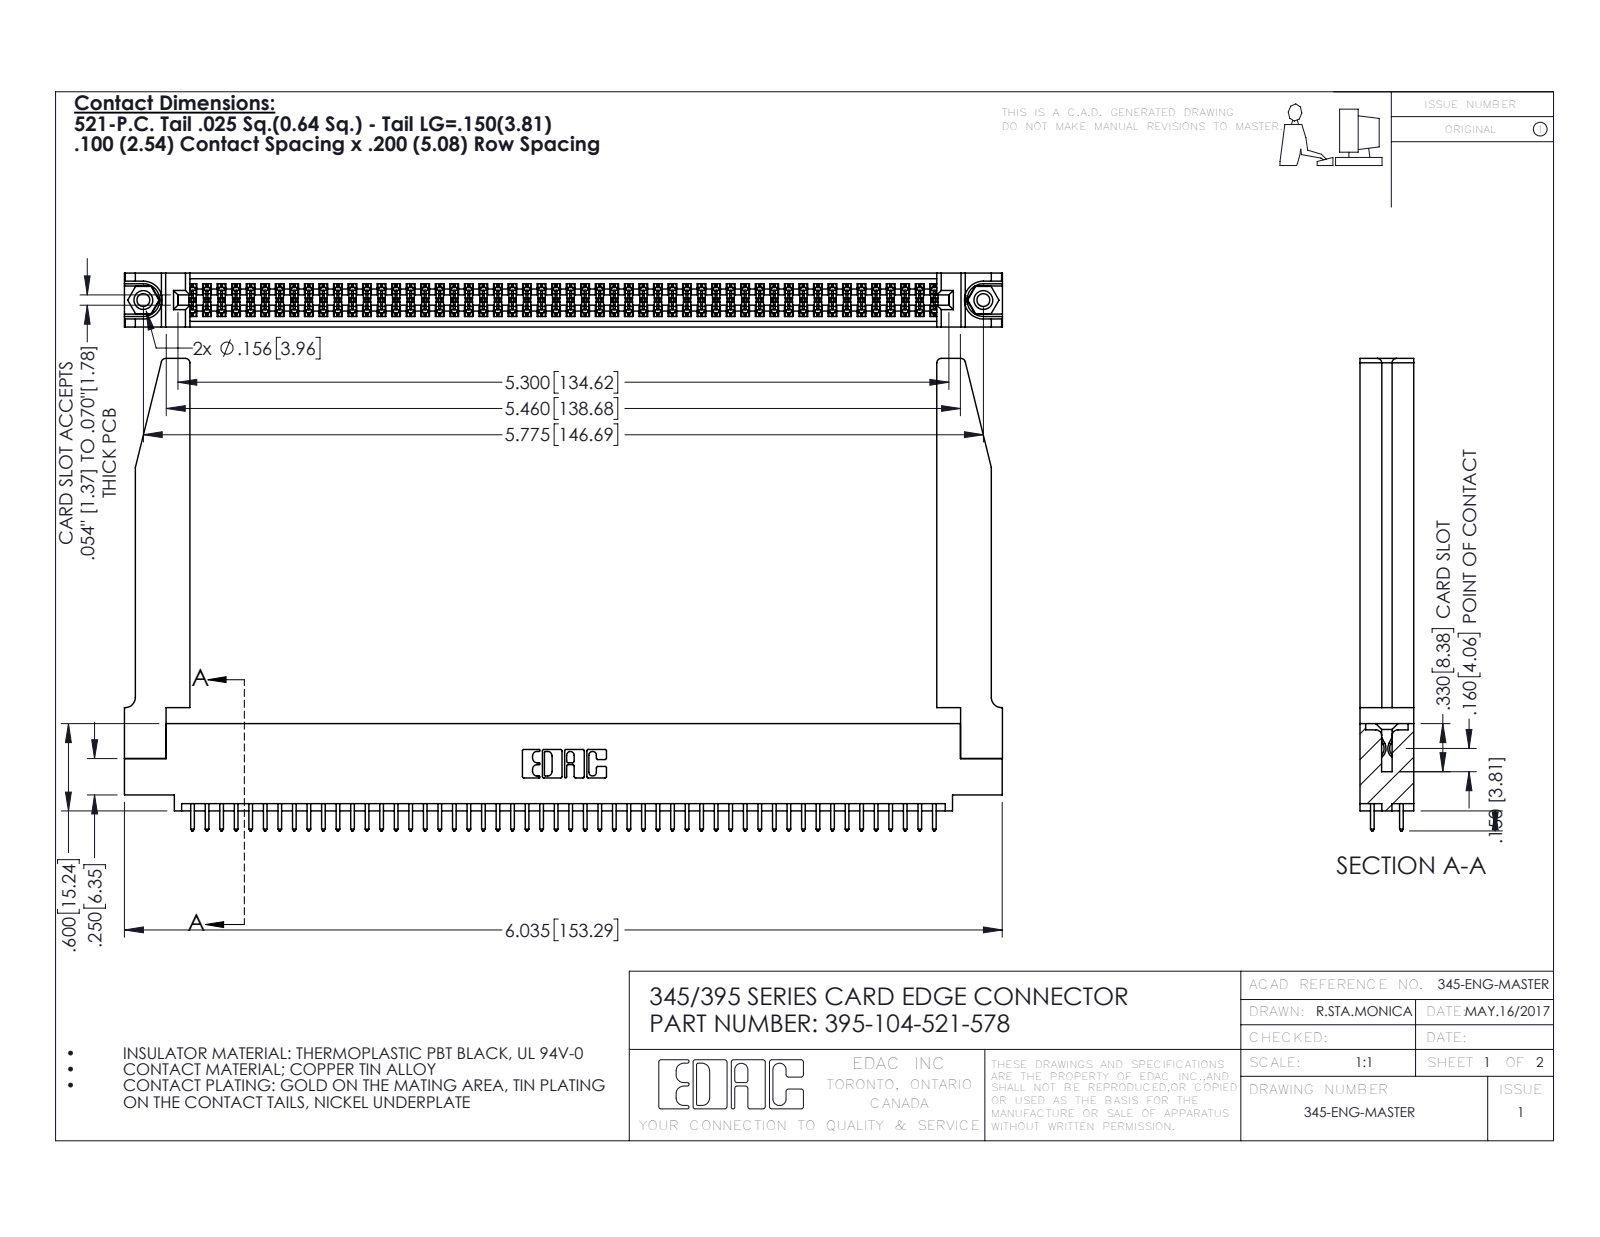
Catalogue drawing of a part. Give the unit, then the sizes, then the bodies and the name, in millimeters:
Units: millimetres
Overall size (bounding box): 153.3 × 82.5 × 9.4
Round holes (diameter × count): ⌀2.3 ×2, ⌀3.2 ×2, ⌀4 ×2, ⌀1.6 ×1
Round bosses / shafts (diameter × count): ⌀3.9 ×2
Partial cylindrical surfaces — rounded edges, fillets, slot ends (radius × count): R0.2 ×156, R0.3 ×104, R0.3 ×22, R0.8 ×8, R0.2 ×6, R0.8 ×6, R0.7 ×3, R0.4 ×2
Main face-to-face distances: 1.8, 7.6, 9.4, 2.5, 6.9, 0.6, 5.1, 5.7, 4.4, 3.8
Hole centre spacings: 6.9, 140.7, 146.7
Volume: 22 650 mm³ · Surface area: 28 830 mm²
Bodies: 109 solids, 5564 faces (3658 planar, 1854 cylindrical, 52 other)
Part name (STEP PRODUCT): 345-250-001_345-250-001-102; 395-104-521-578; 345-220-078_345-220-078; 345 Part_0.110 Offset - 0.156 Dia-TH (+1 more)
STEP written by: SolidWorks 2016 (CONFIG_CONTROL_DESIGN)
